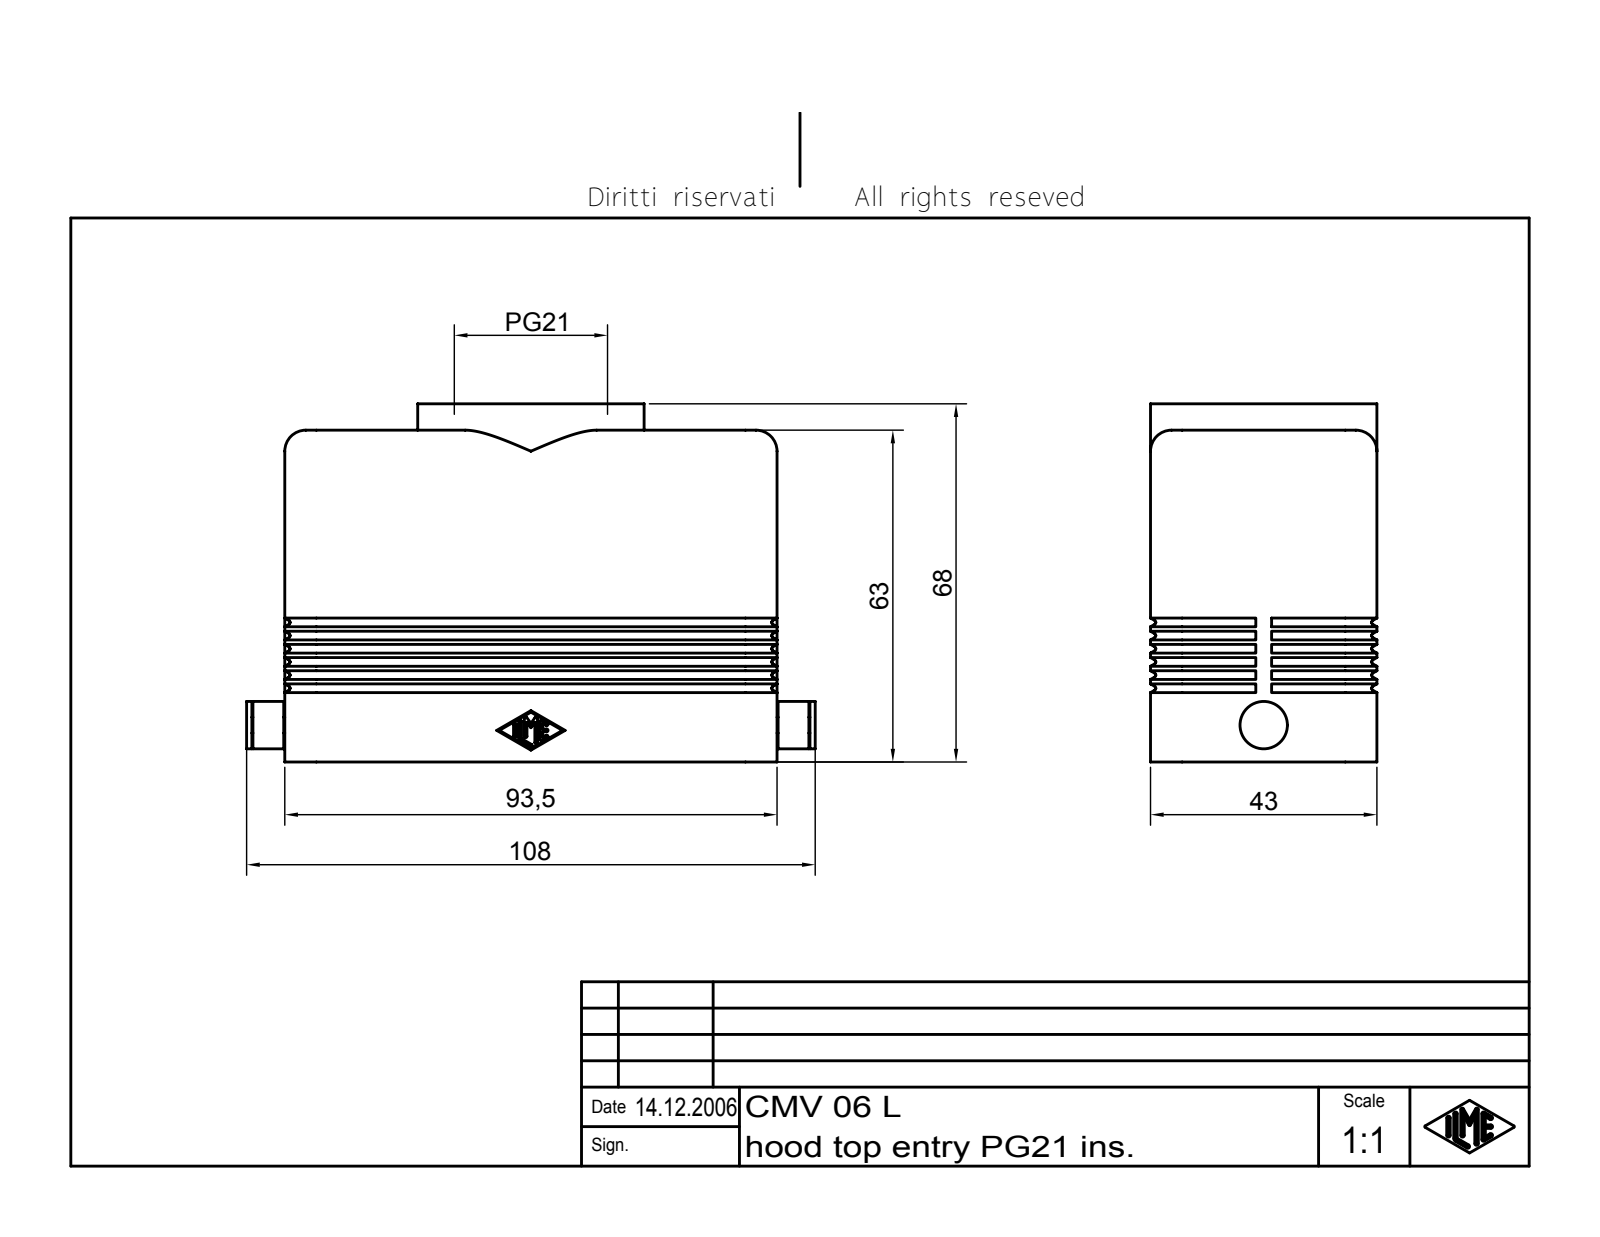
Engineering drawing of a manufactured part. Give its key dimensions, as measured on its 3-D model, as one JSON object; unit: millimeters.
{"part_name": "CMV 06 L", "step_written_by": "Autodesk Inventor 7 (AUTOMOTIVE_DESIGN)", "units": "millimeters", "bodies": {"solids": 1, "faces": 631, "planar": 145, "cylindrical": 268, "other": 218}, "overall_size": [108, 68, 43], "volume_mm3": 72505, "surface_area_mm2": 42038, "round_holes": [[25, 1], [26.78, 1]], "round_bosses_or_shafts": [[43, 1], [9, 1], [3, 1]], "partial_cylinders_radius": [[0.4, 48], [0.25, 14], [1.5, 4], [3, 4], [4, 4], [6, 4], [5, 2]], "face_to_face_distances": [3, 40, 37, 43, 90.5, 93.5, 8.25, 11.25, 82.25, 79.25]}
